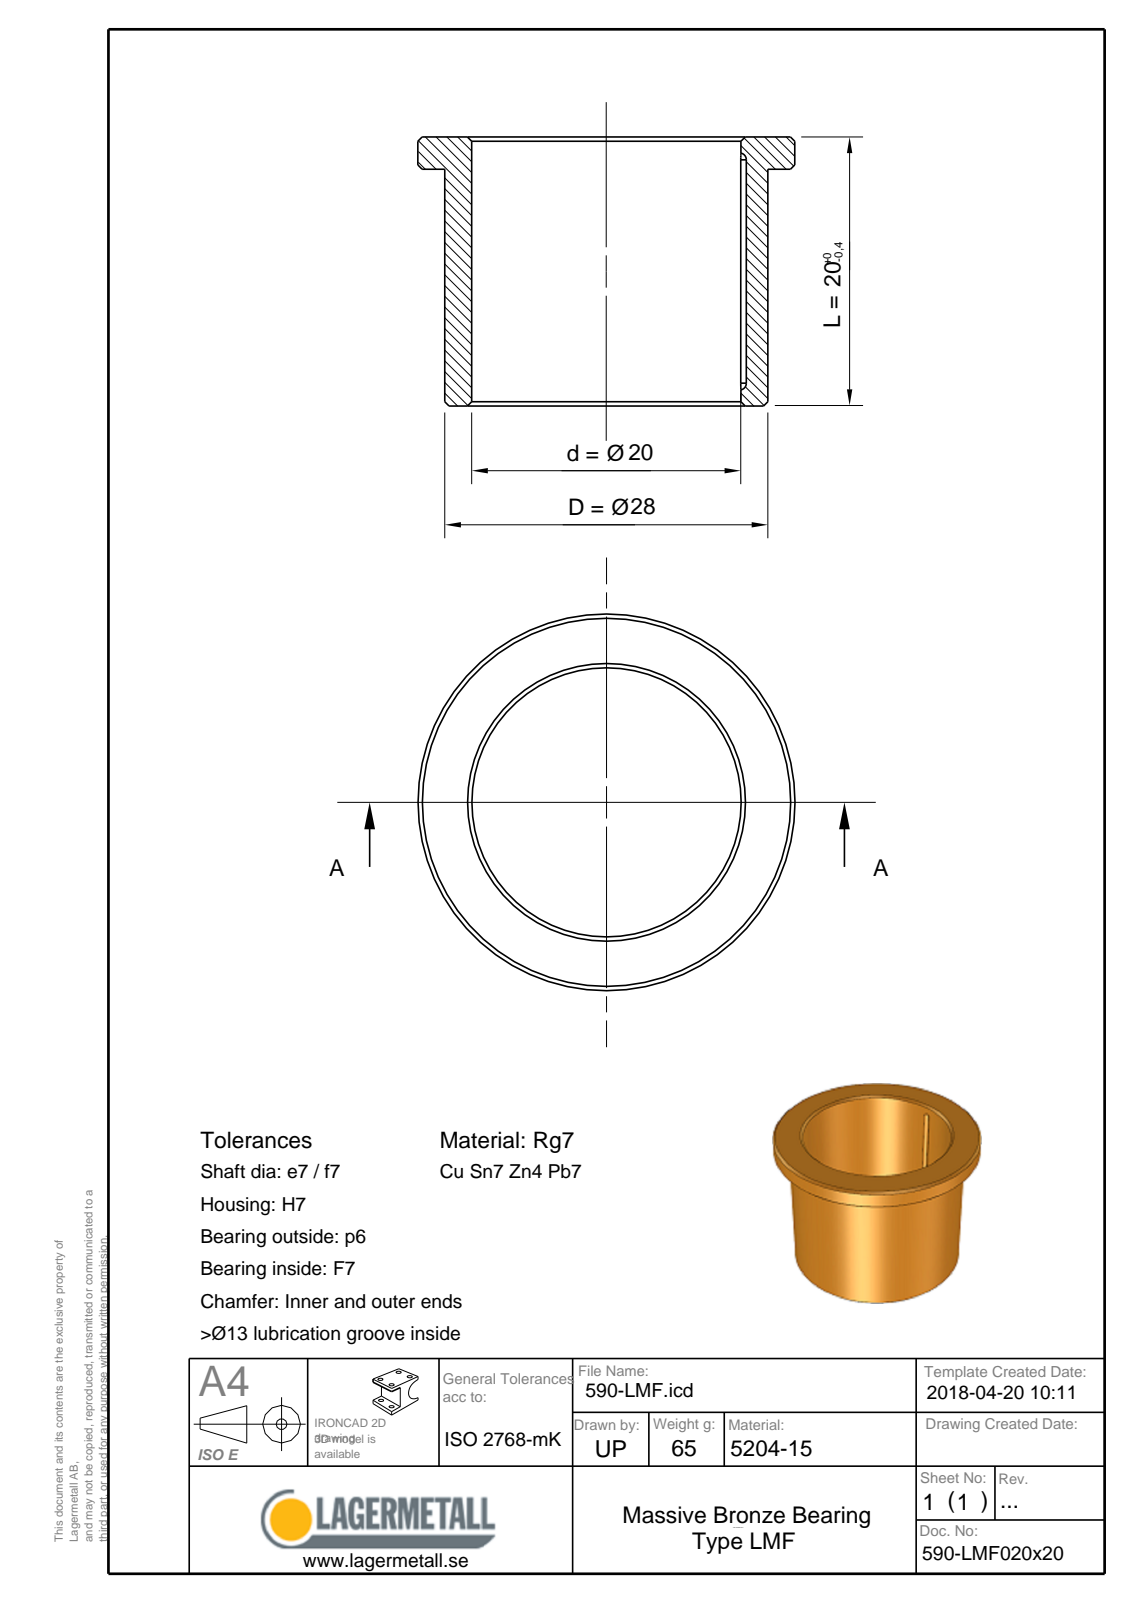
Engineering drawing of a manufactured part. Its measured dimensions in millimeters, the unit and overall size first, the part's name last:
Units: millimetres
Overall size (bounding box): 35 × 35 × 20
Round holes (diameter × count): ⌀20 ×1
Round bosses / shafts (diameter × count): ⌀35 ×1, ⌀28 ×1
Partial cylindrical surfaces — rounded edges, fillets, slot ends (radius × count): R0.75 ×3
Main face-to-face distances: 4, 16, 20, 1.5
Volume: 7 346 mm³ · Surface area: 4 293 mm²
Bodies: 1 solid, 18 faces (5 planar, 6 cylindrical, 7 other)
Part name (STEP PRODUCT): 590-LMF020x20
STEP written by: Spatial InterOp 3D (CONFIG_CONTROL_DESIGN)
